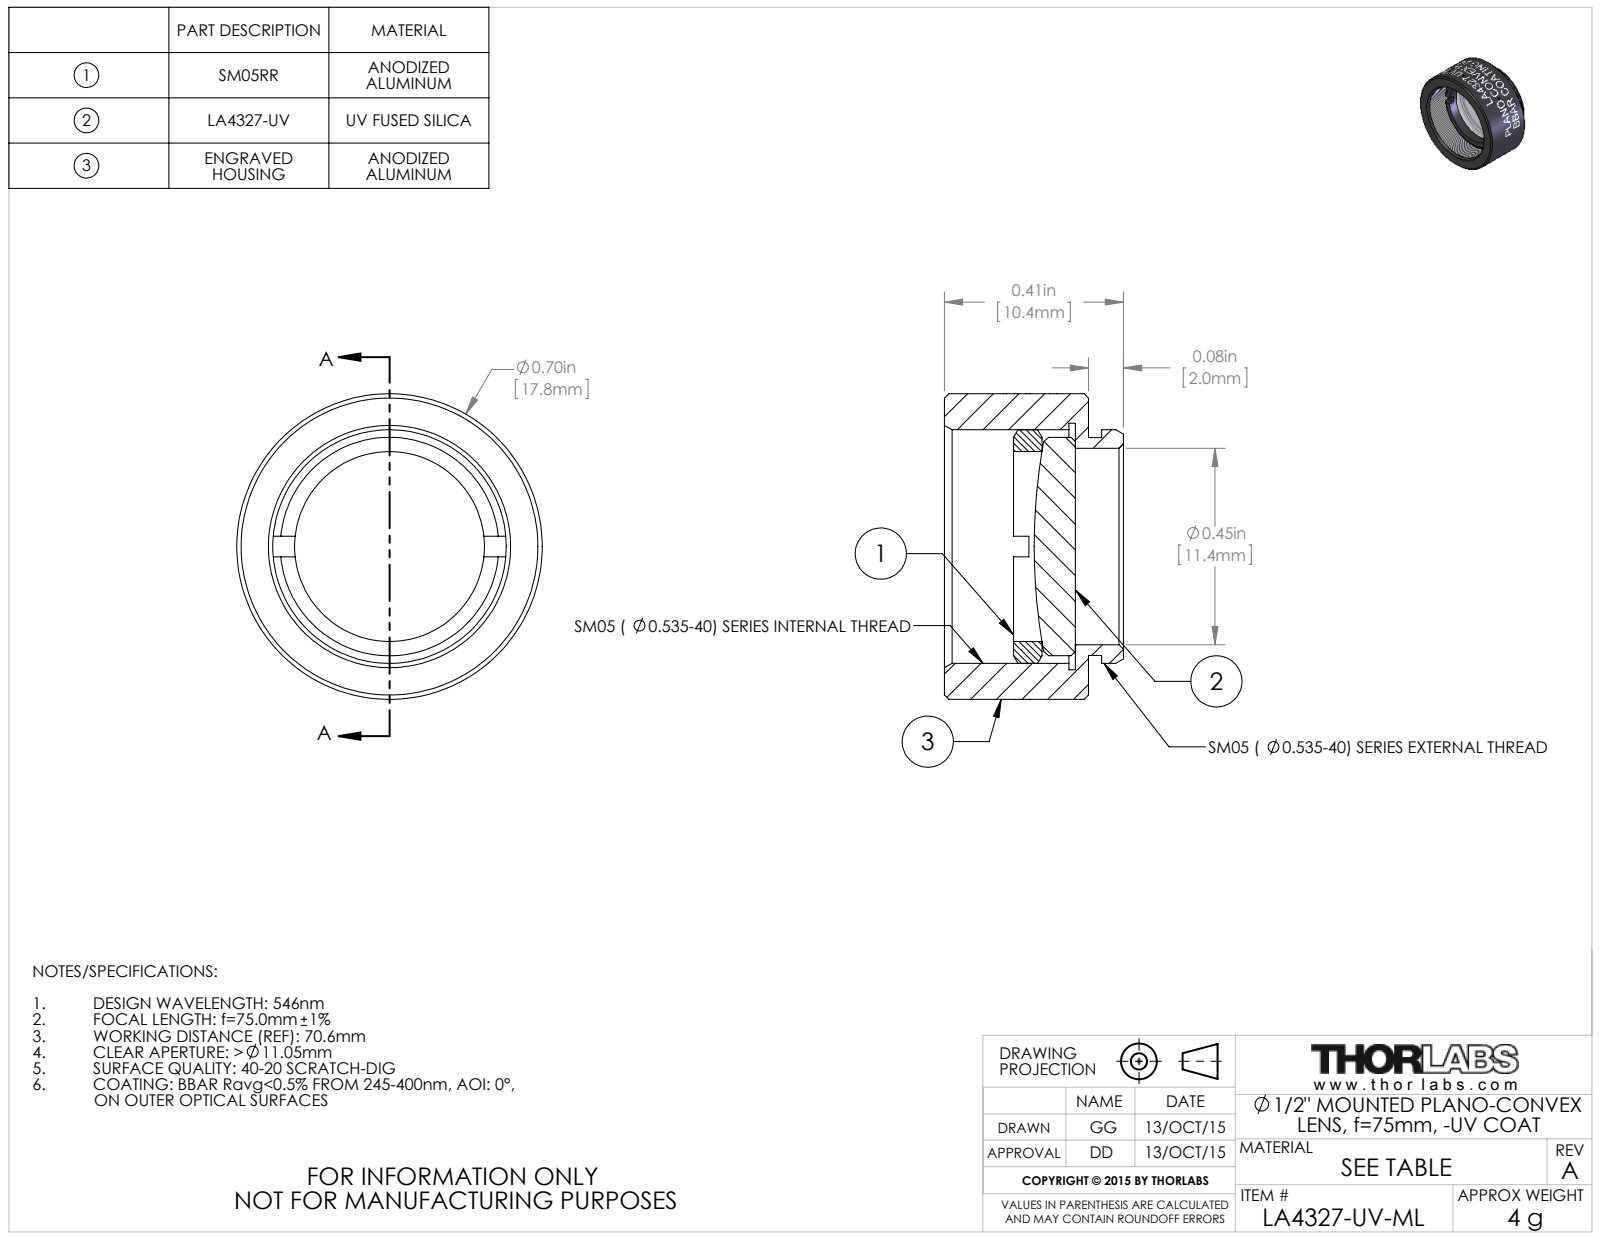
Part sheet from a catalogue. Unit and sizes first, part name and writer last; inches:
Units: inches
Overall size (bounding box): 0.7 × 0.7 × 0.41
Round holes (diameter × count): ⌀0.435 ×1, ⌀0.45 ×1, ⌀0.535 ×1, ⌀0.565 ×1
Round bosses / shafts (diameter × count): ⌀0.7 ×1, ⌀0.535 ×1, ⌀0.5 ×1, ⌀0.499 ×1
Main face-to-face distances: 0.03, 0.33, 0.3, 0.107, 0.077, 0.223, 0.172, 0.142, 0.065, 0.158
Volume: 0.079 in³ · Surface area: 2.837 in²
Bodies: 3 solids, 143 faces (16 planar, 106 cylindrical, 21 other)
Part name (STEP PRODUCT): TTN039243-E0W
STEP written by: SolidWorks 2014 (CONFIG_CONTROL_DESIGN)
